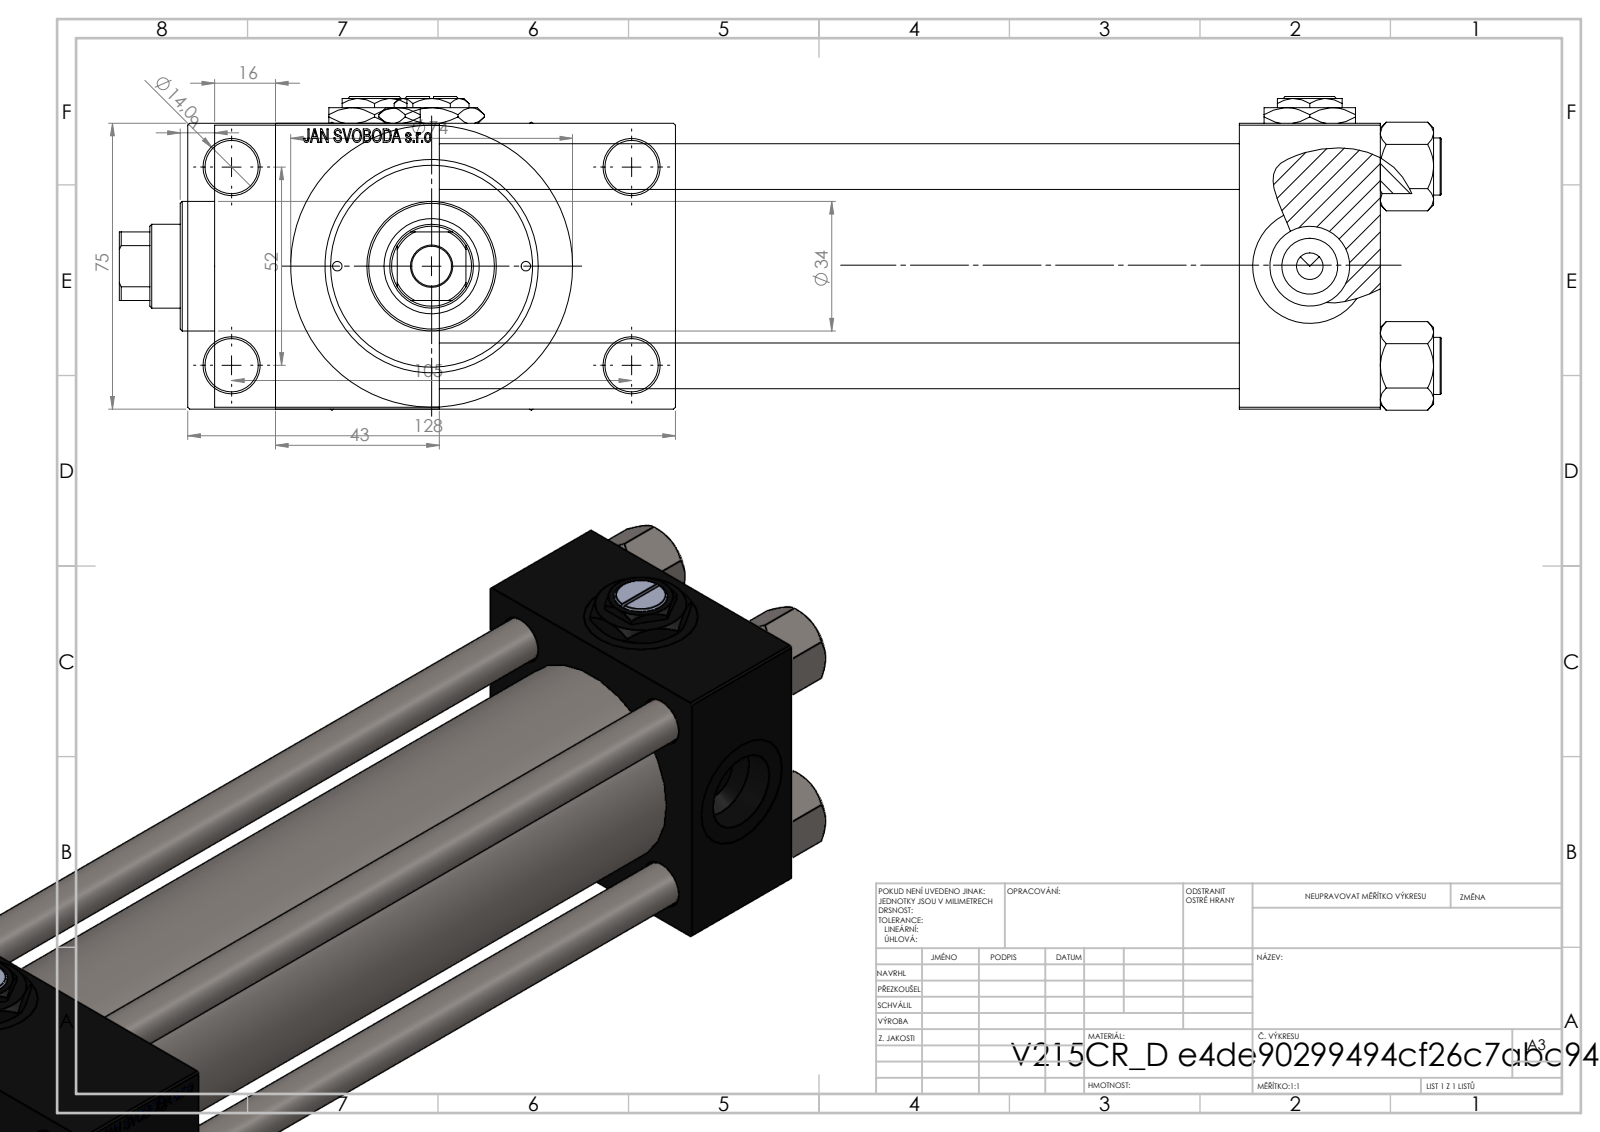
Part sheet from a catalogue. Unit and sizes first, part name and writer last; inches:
Units: inches
Overall size (bounding box): 13.661 × 5.039 × 3.239
Round holes (diameter × count): ⌀0.472 ×4, ⌀0.551 ×4, ⌀0.276 ×3, ⌀0.825 ×3, ⌀1.181 ×3, ⌀0.098 ×2, ⌀0.413 ×1, ⌀0.866 ×1, ⌀0.984 ×1, ⌀1.614 ×1, ⌀1.969 ×1, ⌀2.087 ×1
Round bosses / shafts (diameter × count): ⌀0.591 ×4, ⌀2.913 ×1, ⌀2.205 ×1, ⌀1.339 ×1
Partial cylindrical surfaces — rounded edges, fillets, slot ends (radius × count): R0.413 ×1
Main face-to-face distances: 2.953, 8.268, 1.457, 9.724, 1.043, 3.996, 11.417, 9.961, 1.693, 0.63
Hole centre spacings: 1.031, 1.037, 1.456, 1.497, 2.059, 2.253, 2.3, 2.307
Volume: 61.33 in³ · Surface area: 392.2 in²
Bodies: 13 solids, 1212 faces (547 planar, 103 cylindrical, 562 other)
Part name (STEP PRODUCT): Zatka_pro_OIL_PORT; V215CR_D_TYCINKA; V215CR_VCP_D; V215CR_D_Body (+2 more)
STEP written by: SolidWorks 2019 (CONFIG_CONTROL_DESIGN)
